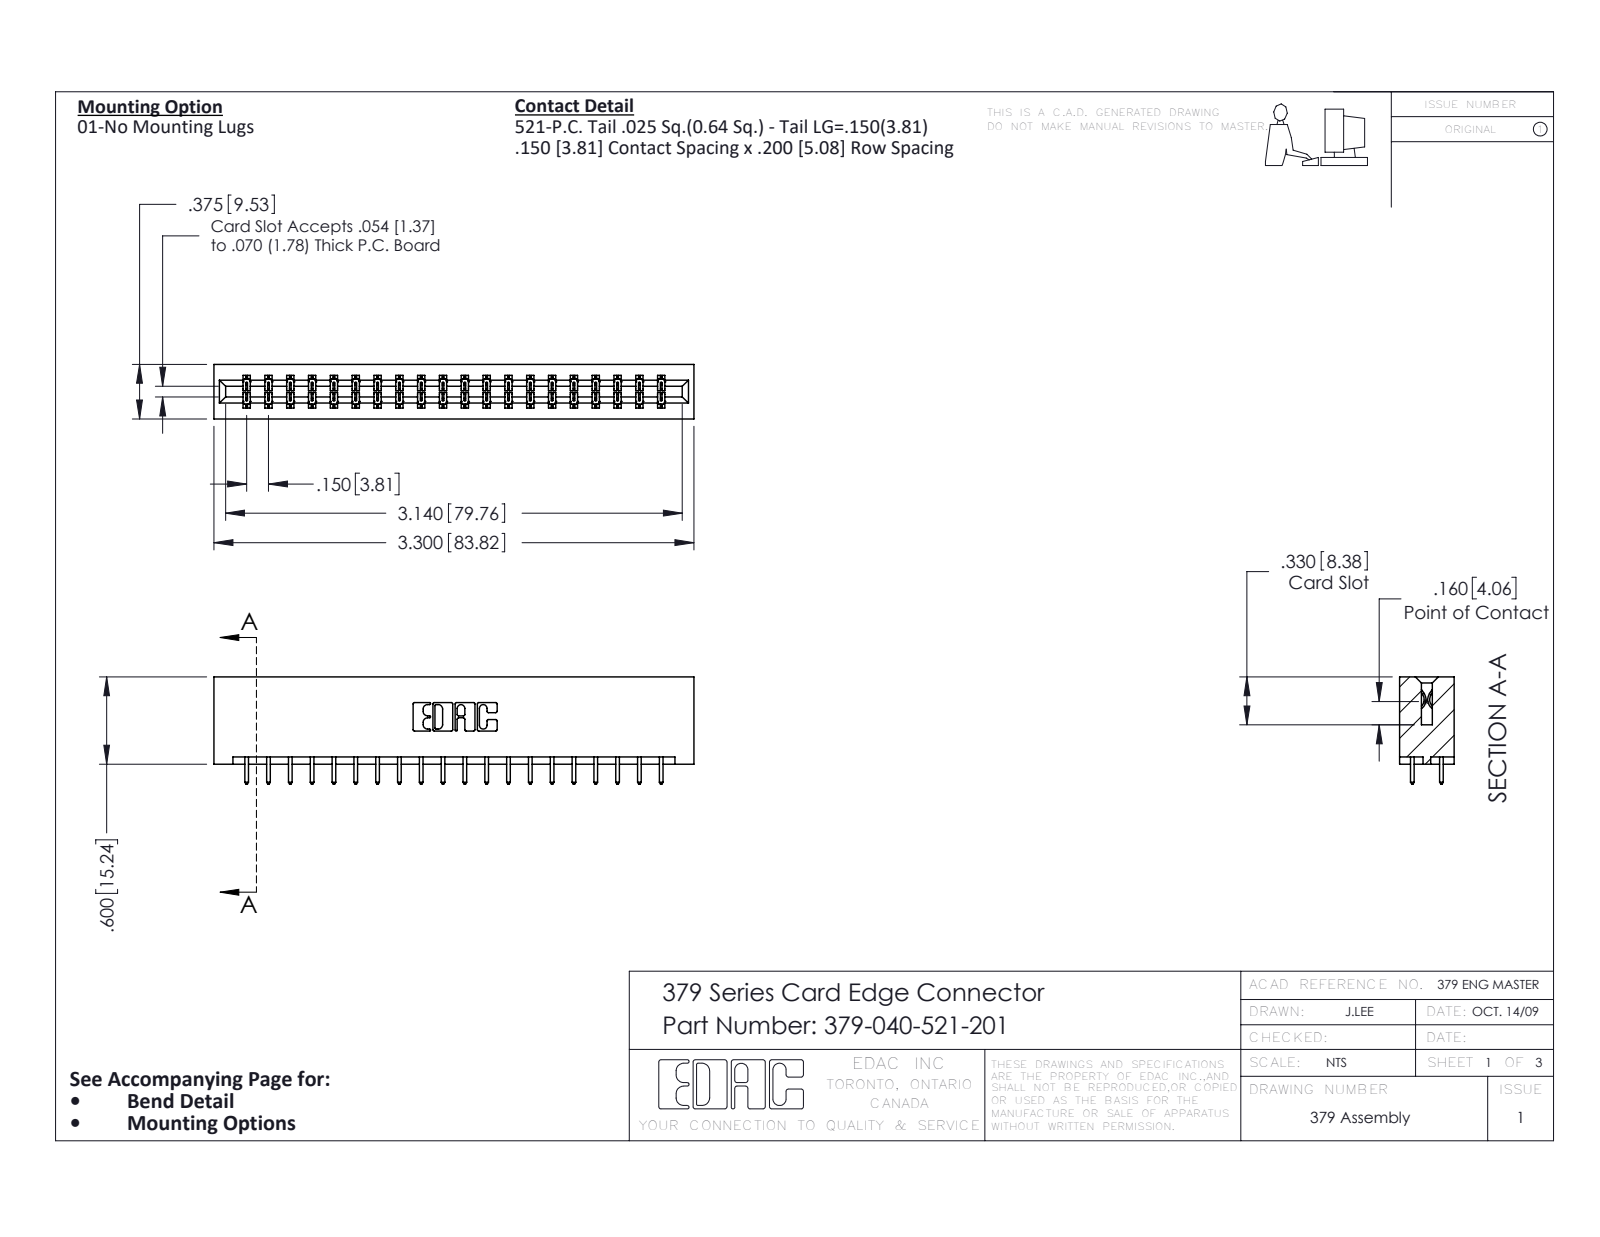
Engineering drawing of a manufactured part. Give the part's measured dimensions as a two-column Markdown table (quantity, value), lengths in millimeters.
| quantity | value |
| --- | --- |
| part name | 379 Part_Lugless; 379-040-521-201; 345-292-001_345-293-121 |
| STEP written by | SolidWorks 2016 (CONFIG_CONTROL_DESIGN) |
| units | millimeters |
| bodies | 41 solids, 2186 faces (1506 planar, 680 cylindrical, 0 other) |
| overall size | 83.8 × 18.7 × 9.5 |
| volume | 9 370 mm³ |
| surface area | 10 250 mm² |
| partial cylindrical surfaces (radius × count) | 0.2 × 60, 0.3 × 40, 0.3 × 22, 0.2 × 6, 0.8 × 6, 0.7 × 3, 0.4 × 2, 0.6 × 2 |
| main face-to-face distances | 7.6, 1.9, 9.5, 5.1, 2.5, 3.8, 5.7, 14, 15.2, 1.9 |
